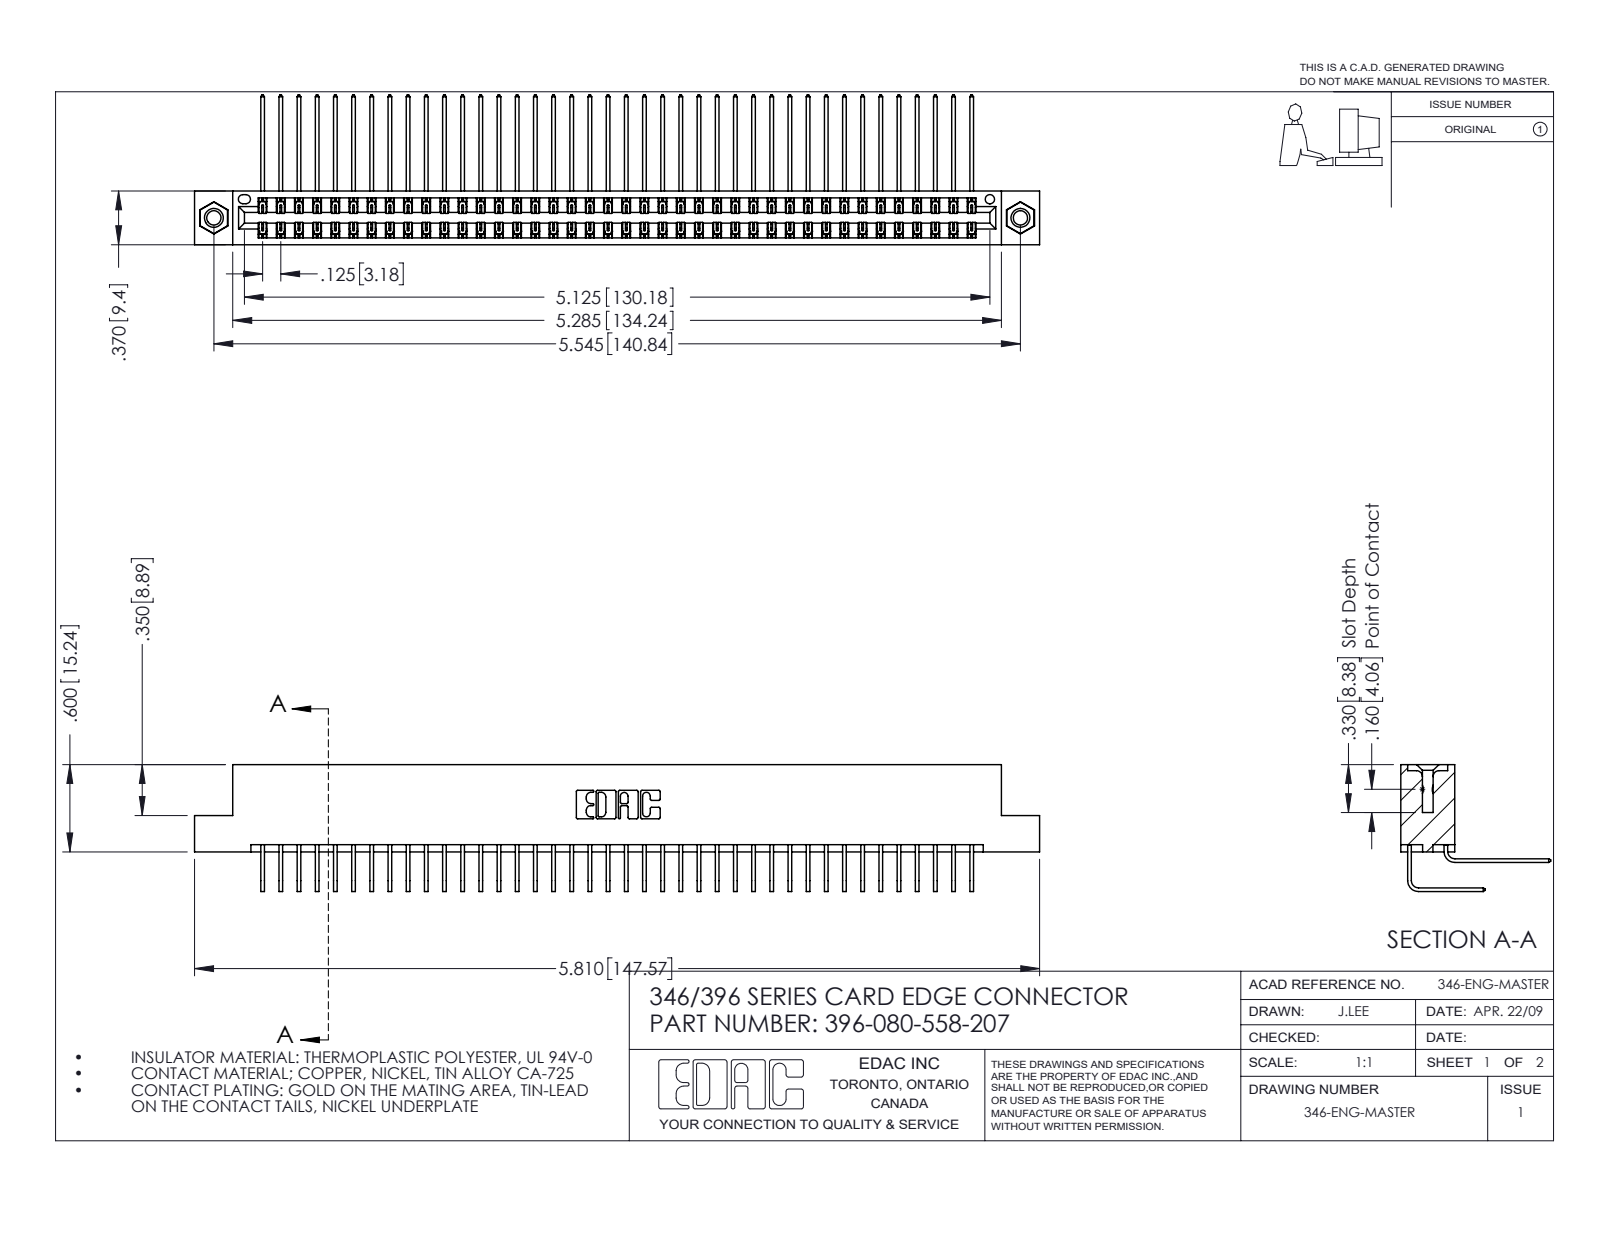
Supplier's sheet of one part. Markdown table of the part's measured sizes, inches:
| quantity | value |
| --- | --- |
| part name | 345-292-001_558 Tail - 2; 345-250-001_345-250-005-103; 346 Part_Flush Mounting Lugs - 0.156 Dia-TI; 345-292-001_558 559 Tail - 1 (+1 more) |
| STEP written by | SolidWorks 2016 (CONFIG_CONTROL_DESIGN) |
| units | inches |
| bodies | 83 solids, 4502 faces (3068 planar, 1418 cylindrical, 16 other) |
| overall size | 5.81 × 1.03 × 0.873 |
| volume | 0.905 in³ |
| surface area | 35.02 in² |
| round holes (diameter × count) | 0.098 × 2, 0.125 × 2, 0.156 × 2, 0.064 × 1 |
| round bosses / shafts (diameter × count) | 0.155 × 2 |
| partial cylindrical surfaces (radius × count) | 0.006 × 120, 0.01 × 22, 0.007 × 6, 0.031 × 6, 0.026 × 3, 0.014 × 2, 0.022 × 2, 0.024 × 2 |
| main face-to-face distances | 0.048, 0.322, 0.025, 0.37, 0.25, 0.072, 0.298, 0.275, 0.148, 0.222 |
| hole center spacings | 0.246, 5.336, 5.545 |
